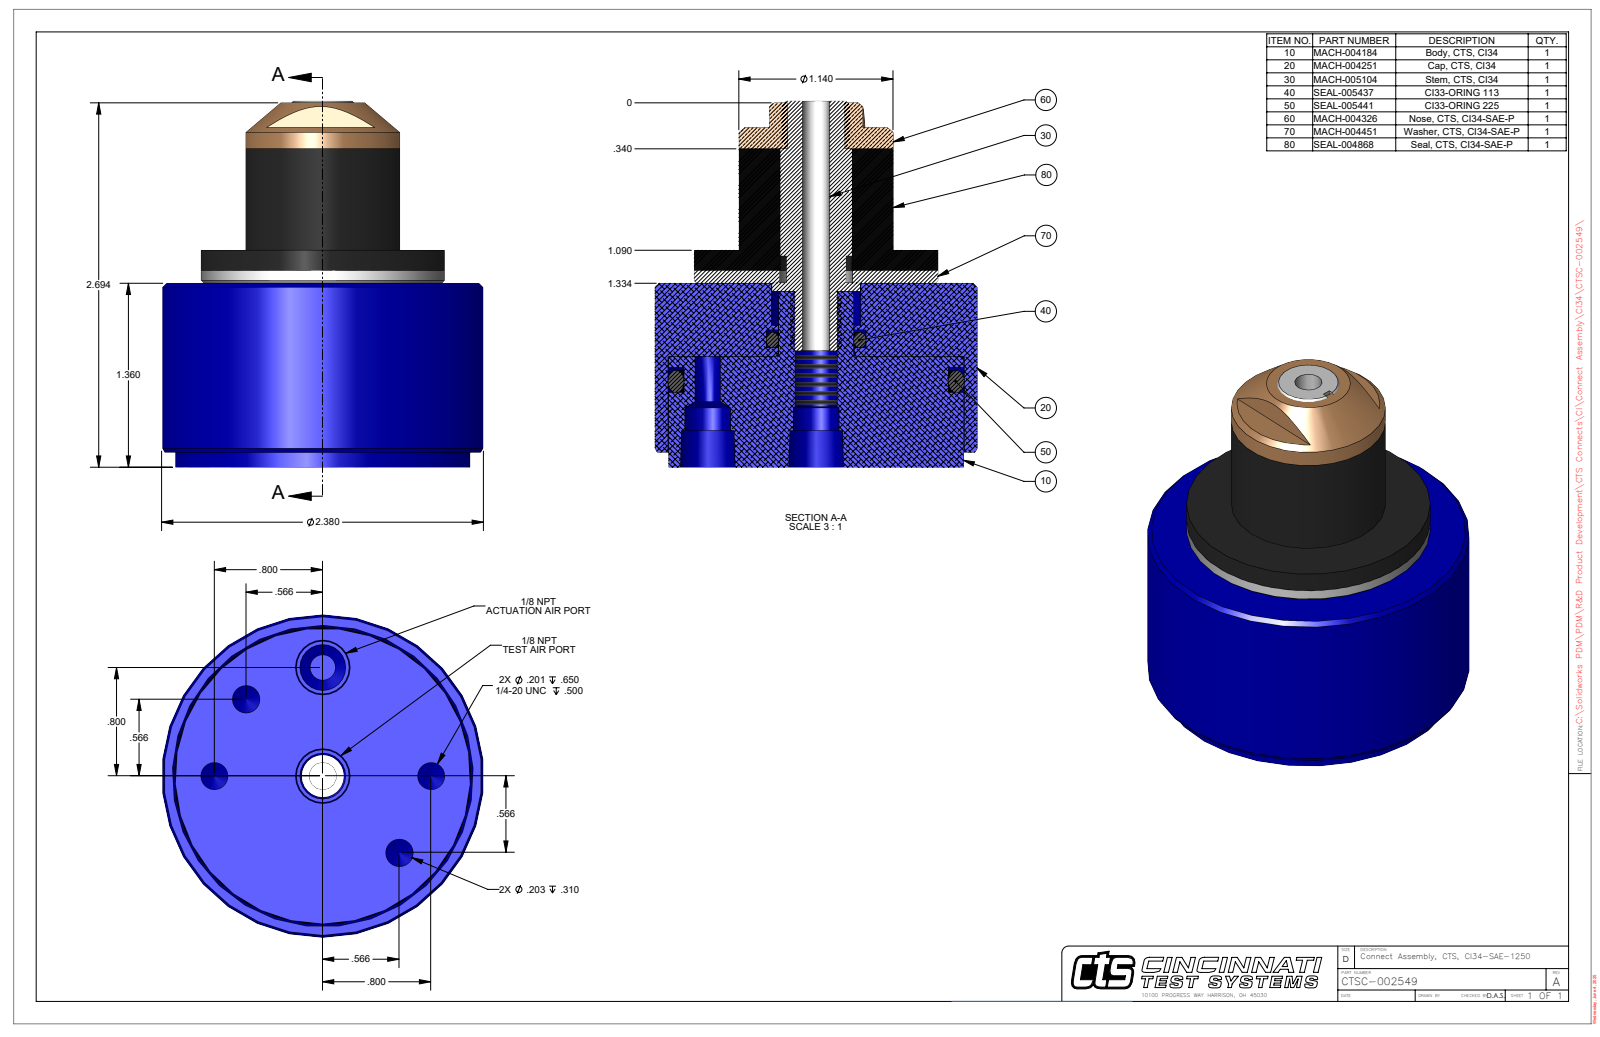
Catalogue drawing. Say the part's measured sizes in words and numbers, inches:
The part is named "CTSC-002549". Its 3-D file was written by "SolidWorks 2023 (AUTOMOTIVE_DESIGN)". It is 1 solid with 77 faces: 23 planar, 29 cylindrical and 25 other. Overall it measures 2.706 by 2.38 by 2.38 inches. Its volume is 7.365 cubic inches and its surface area 31.78 square inches. Round holes: 2 of diameter 0.201, 2 of diameter 0.203, 2 of diameter 0.339, 1 of diameter 0.203, 1 of diameter 0.661, 1 of diameter 2.188. Round bosses or shafts: 1 of diameter 2.38, 1 of diameter 2.178, 1 of diameter 1.8, 1 of diameter 1.14, 1 of diameter 0.65. Partial cylindrical surfaces (rounded edges, fillets, slot ends): 1 of radius 0.211. The main face-to-face distances are 1.36, 1.604, 0.244, 0.11, 1.25, 1.494, 0.448, 0.338, 0.912, 1.156. The hole center spacings are 0.8, 0.612, 1.478, 1.131, 1.6.
